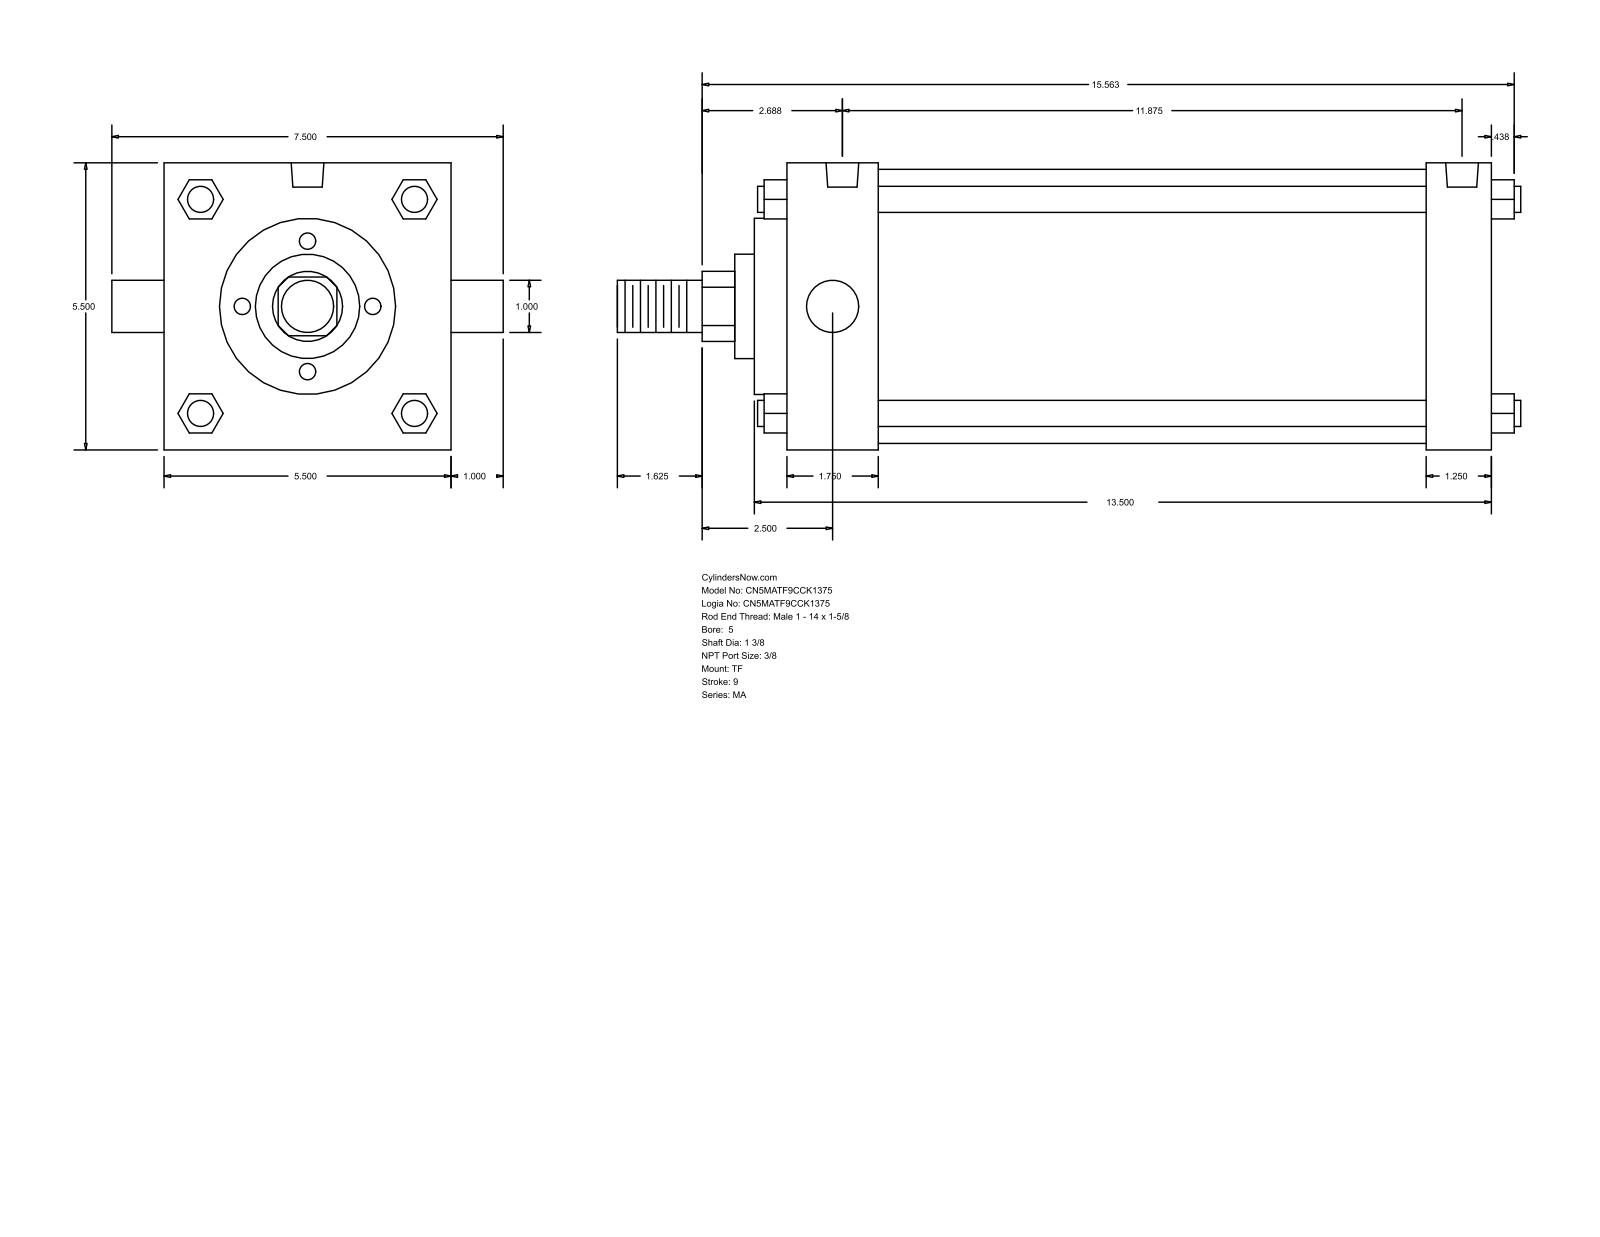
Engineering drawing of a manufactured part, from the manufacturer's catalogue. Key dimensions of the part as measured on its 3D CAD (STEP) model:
Part name (STEP PRODUCT): MA_TF__0500_1.375
STEP written by: GSSL Pune (CONFIG_CONTROL_DESIGN)
Units: millimetres
Bodies: 0 solids, 122 faces (93 planar, 29 cylindrical, 0 other)
Overall size (bounding box): 439.74 × 190.5 × 139.7
Round holes (diameter × count): ⌀11.11 ×3, ⌀15.93 ×2
Round bosses / shafts (diameter × count): ⌀12.7 ×4, ⌀25.4 ×2, ⌀133.35 ×1, ⌀85.72 ×1, ⌀50.8 ×1, ⌀34.92 ×1
Partial cylindrical surfaces — rounded edges, fillets, slot ends (radius × count): R17.06 ×1
Main face-to-face distances: 139.7, 342.91, 311.16, 31.75, 44.45, 266.71, 298.46, 15.87, 60.32, 327.03
Hole centre spacings: 4.77, 296.86, 292.09, 301.63
